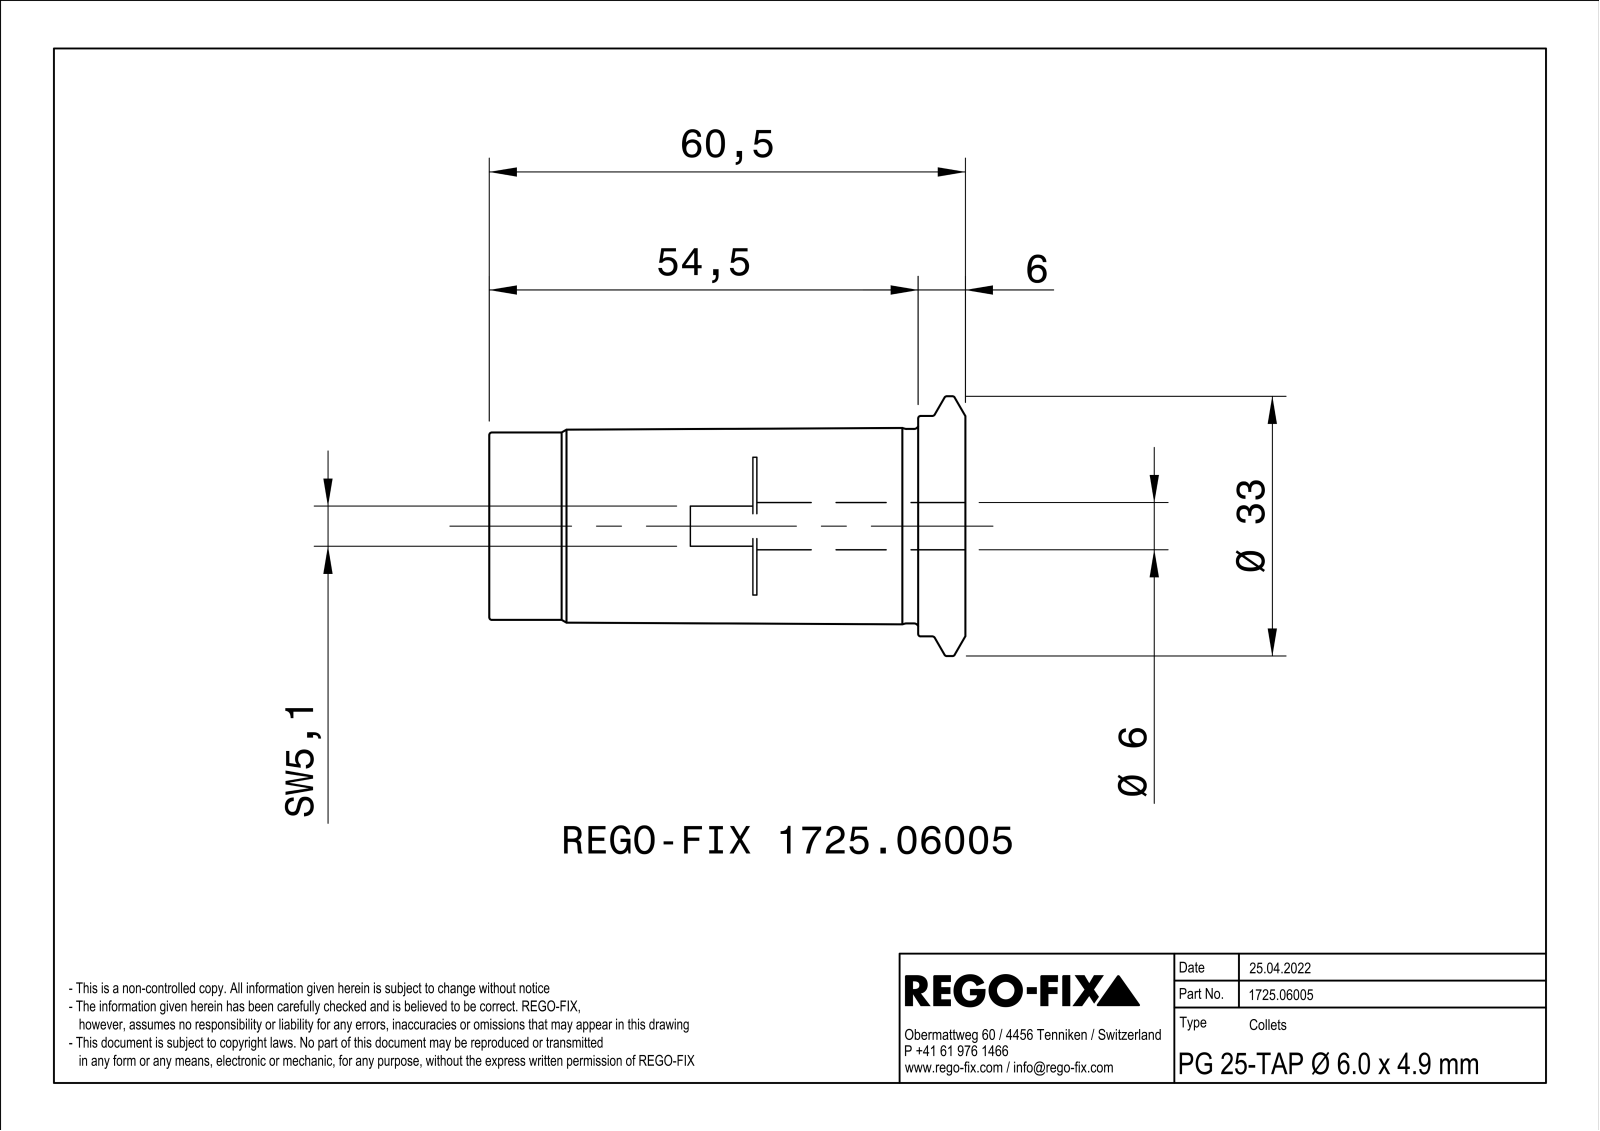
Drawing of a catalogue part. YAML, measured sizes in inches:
part_name: "NOCUT"
step_written_by: "SIEMENS PLM Software Solid Edge ST10 (AUTOMOTIVE_DESIGN)"
units: inches
bodies: {solids: 1, faces: 49, planar: 21, cylindrical: 15, other: 13}
overall_size: [2.382, 1.299, 1.299]
volume: 1.72
surface_area: 11.43
round_holes:
  - {diameter: 0.236, count: 1}
  - {diameter: 0.272, count: 1}
  - {diameter: 0.276, count: 1}
round_bosses_or_shafts:
  - {diameter: 1.299, count: 1}
  - {diameter: 1.102, count: 1}
  - {diameter: 0.972, count: 1}
  - {diameter: 0.937, count: 1}
partial_cylinders:
  - {radius: 0.11, count: 1}
  - {radius: 0.124, count: 1}
face_to_face_distances: [2.382, 0.236, 2.146, 0.205, 1.398, 1.161, 0.984, 1.063, 0.827, 0.335]
